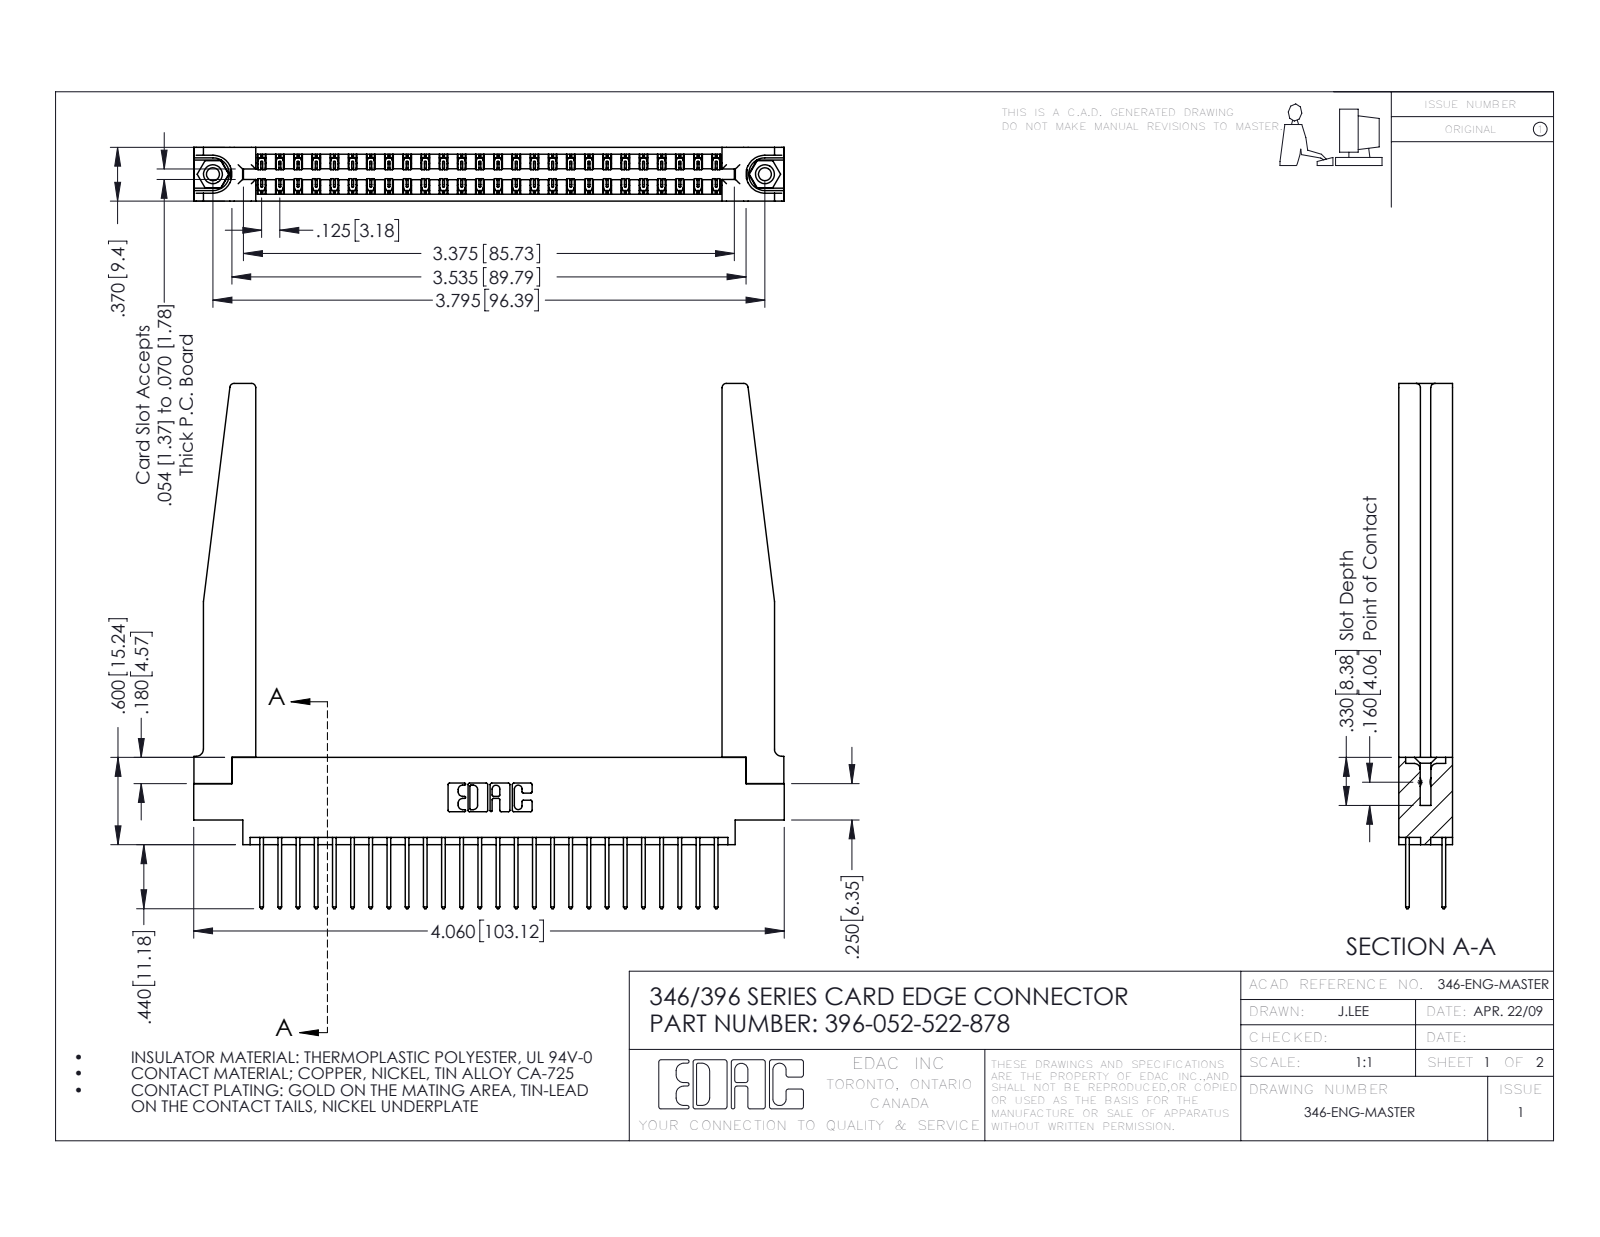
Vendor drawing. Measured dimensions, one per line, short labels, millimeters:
name: 396-052-522-878; 345-250-001_345-250-001-102; 346 Part_0.170 Offset - 0.156 Dia-TH; 346-220-078_345-220-078 (+1 more)
written by: SolidWorks 2016 (CONFIG_CONTROL_DESIGN)
unit: mm
bodies: 57 solids, 3064 faces (2042 planar, 970 cylindrical, 52 other)
size: 103.1 × 91.7 × 9.4
volume: 16 810 mm³; area: 20 700 mm²
holes: 2× ⌀2.3, 2× ⌀3.2, 2× ⌀4, 1× ⌀1.6
bosses: 2× ⌀3.9
rounds: 78× R0.2, 52× R0.3, 22× R0.3, 8× R0.8, 6× R0.2, 6× R0.8, 3× R0.7, 2× R0.4
face distances: 9.4, 1.2, 8.2, 1.8, 6.4, 3.8, 3.8, 7.6, 0.6, 7
hole spacings: 6.2, 91.1, 96.4
